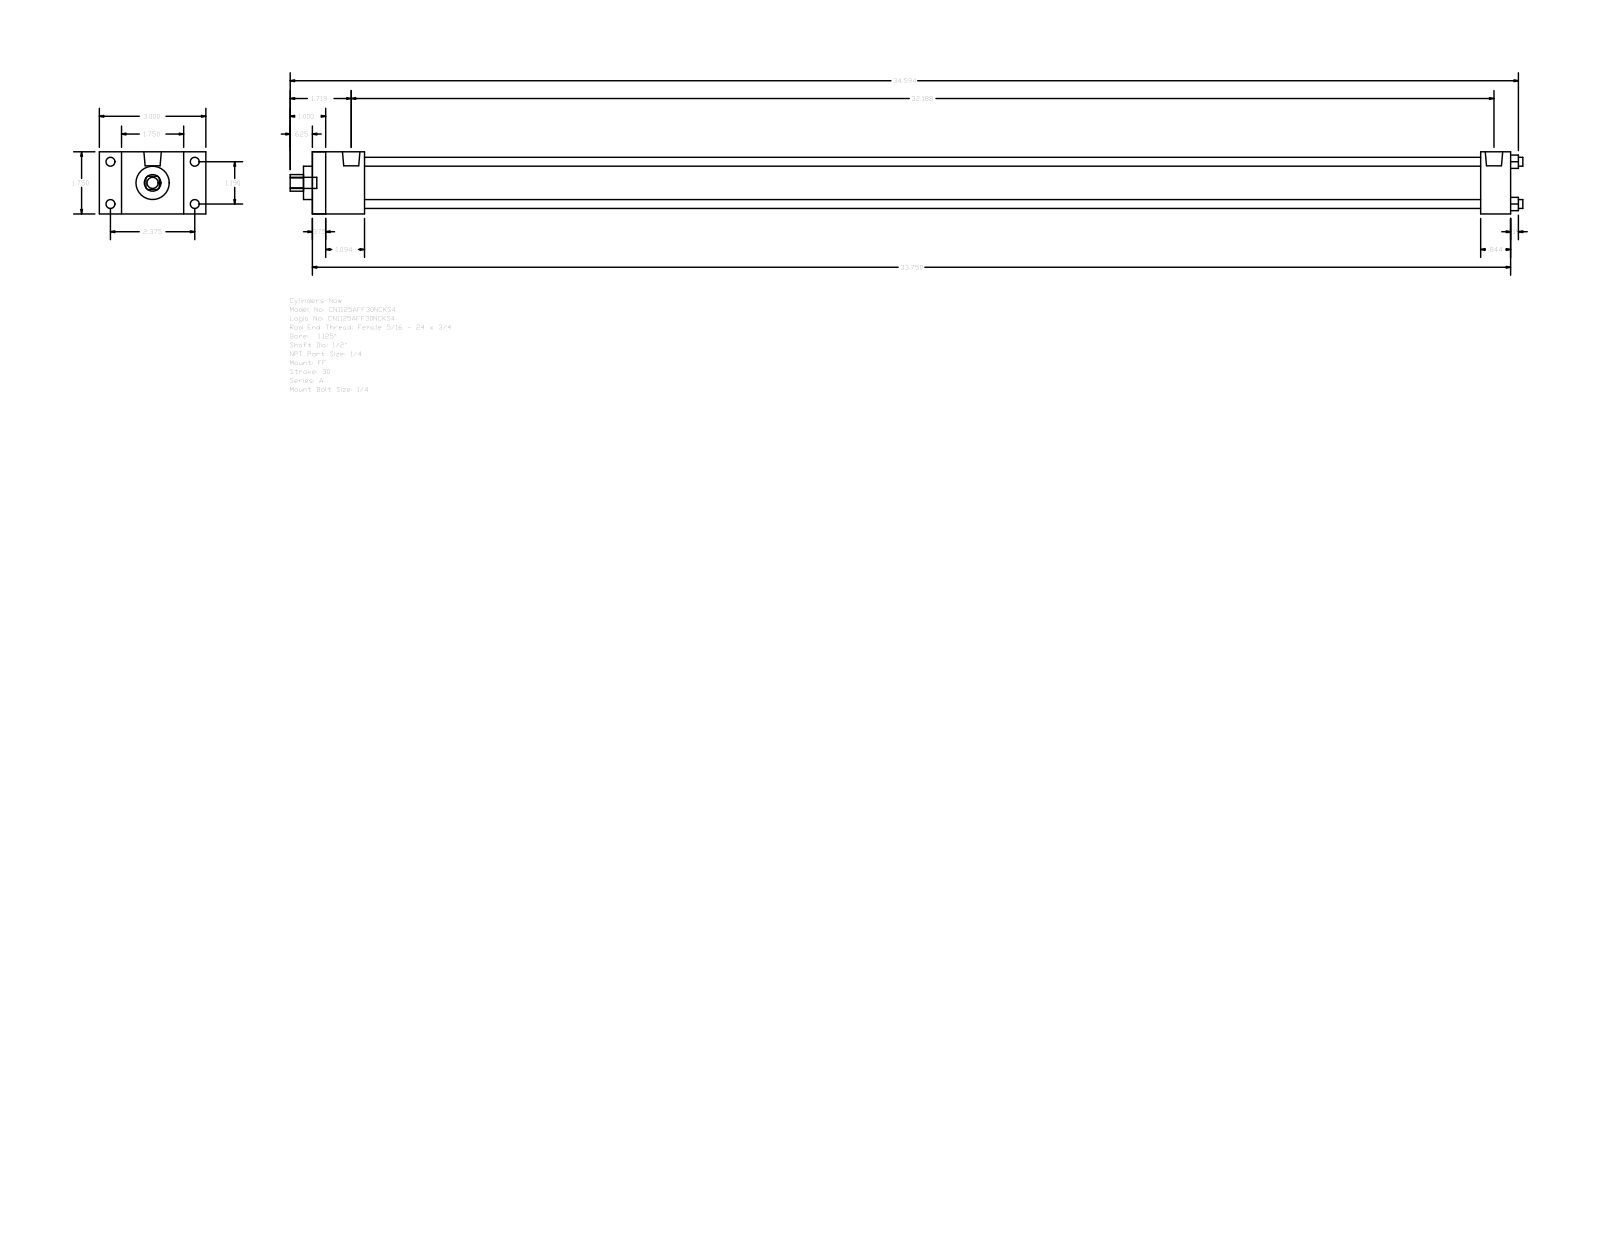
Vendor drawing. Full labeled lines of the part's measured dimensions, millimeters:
Part name (STEP PRODUCT): A_FF__0112_0.5
STEP written by: GSSL Pune (CONFIG_CONTROL_DESIGN)
Units: millimetres
Bodies: 0 solids, 92 faces (64 planar, 28 cylindrical, 0 other)
Overall size (bounding box): 881.86 × 76.2 × 44.45
Round holes (diameter × count): ⌀6.35 ×4, ⌀12.7 ×1, ⌀23.81 ×1, ⌀31.88 ×1
Round bosses / shafts (diameter × count): ⌀6.35 ×4, ⌀5.56 ×4, ⌀12.49 ×2, ⌀7.94 ×1
Partial cylindrical surfaces — rounded edges, fillets, slot ends (radius × count): R5.94 ×1
Main face-to-face distances: 44.46, 857.24, 9.52, 847.72, 15.87, 835.81, 826.29, 21.43, 37.3, 27.78
Hole centre spacings: 21.37, 30.22, 42.74
